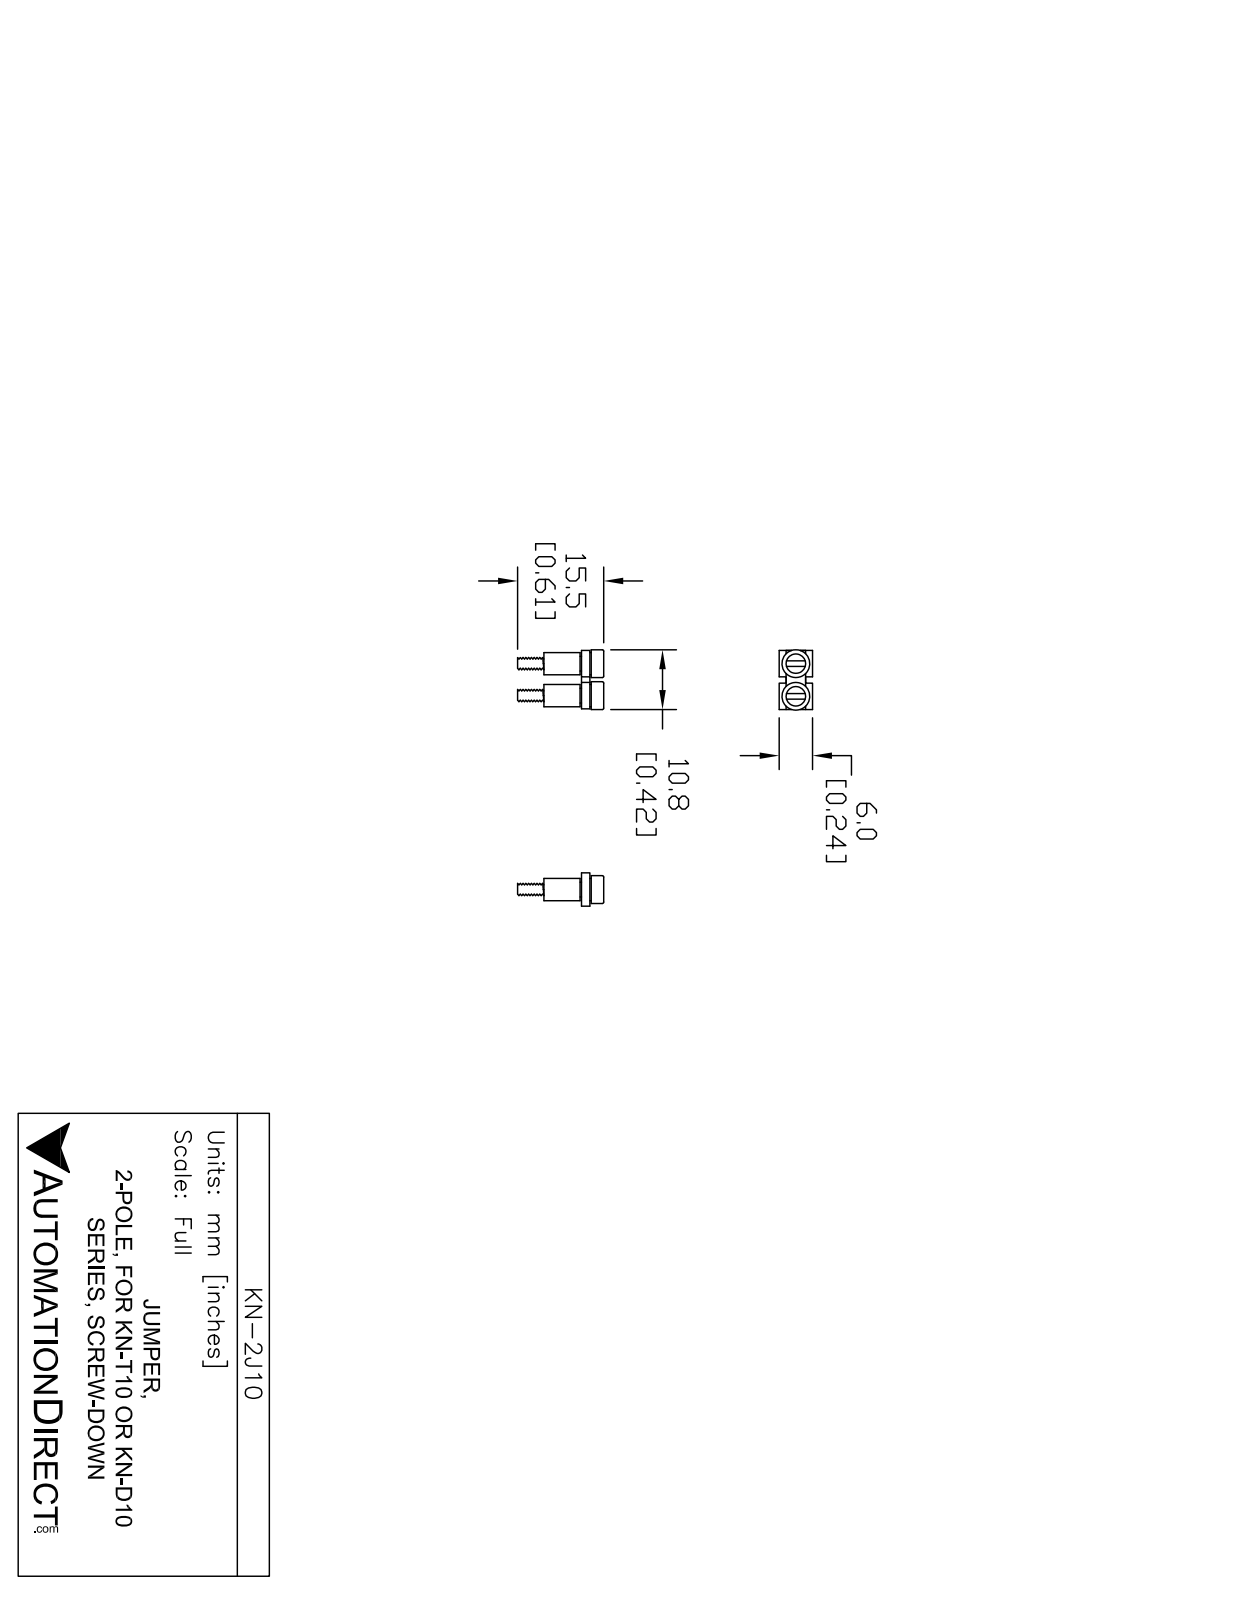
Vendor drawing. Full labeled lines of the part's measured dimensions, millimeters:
Part name (STEP PRODUCT): KN-2J10
STEP written by: SolidWorks 2014 (AUTOMOTIVE_DESIGN)
Units: millimetres
Bodies: 7 solids, 82 faces (40 planar, 30 cylindrical, 12 other)
Overall size (bounding box): 15.5 × 11 × 6
Volume: 360 mm³ · Surface area: 992 mm²
Round holes (diameter × count): ⌀3 ×2, ⌀3.15 ×2, ⌀3.5 ×2
Round bosses / shafts (diameter × count): ⌀5 ×2, ⌀4 ×2, ⌀2.65 ×2
Main face-to-face distances: 1.5, 1.75, 6, 2, 1, 2.5, 4.75, 10.75, 3.5, 0.5
Hole centre spacings: 6
